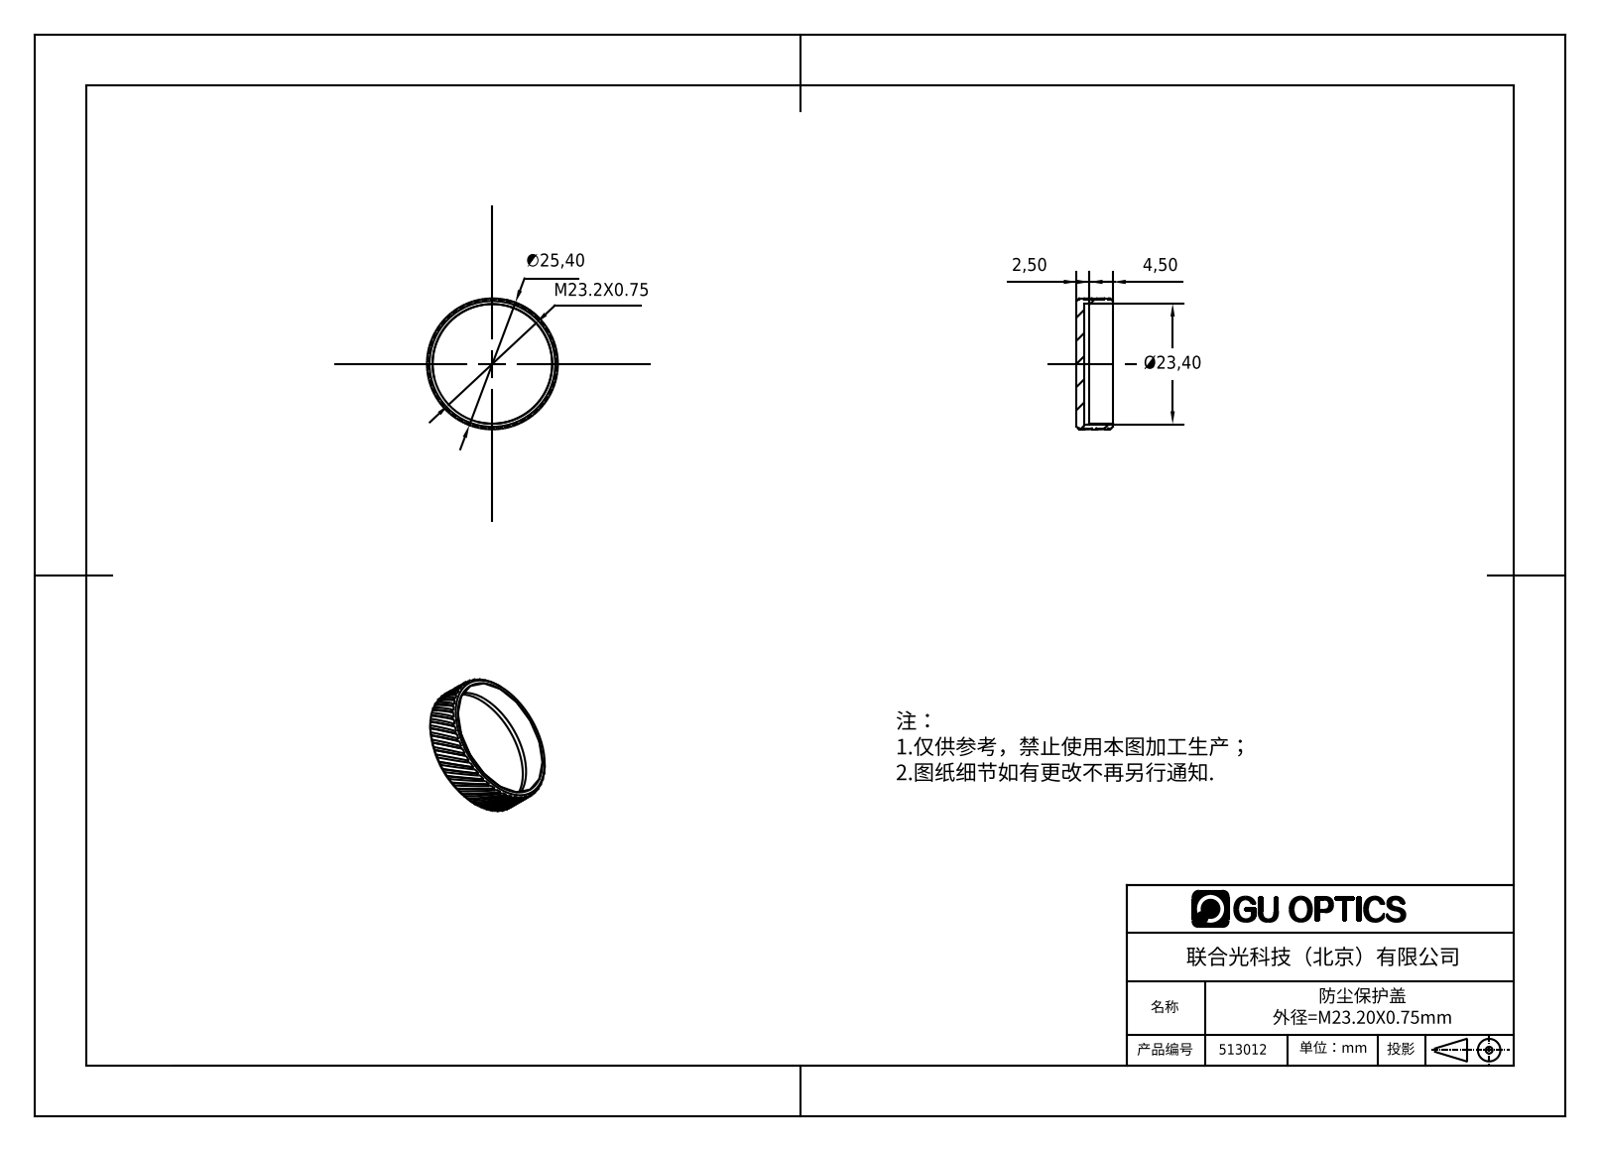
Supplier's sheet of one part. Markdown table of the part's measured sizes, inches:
| quantity | value |
| --- | --- |
| part name | 513012 |
| STEP written by | SolidWorks 2016 (AUTOMOTIVE_DESIGN) |
| units | inches |
| bodies | 1 solid, 215 faces (104 planar, 107 cylindrical, 4 other) |
| overall size | 1 × 1 × 0.276 |
| volume | 0.069 in³ |
| surface area | 3.236 in² |
| round holes (diameter × count) | 0.913 × 1, 0.921 × 1 |
| round bosses / shafts (diameter × count) | 1 × 1, 0.984 × 1 |
| main face-to-face distances | 0.059, 0.031, 0.217, 0.276, 0.177, 0.039, 0.098 |
